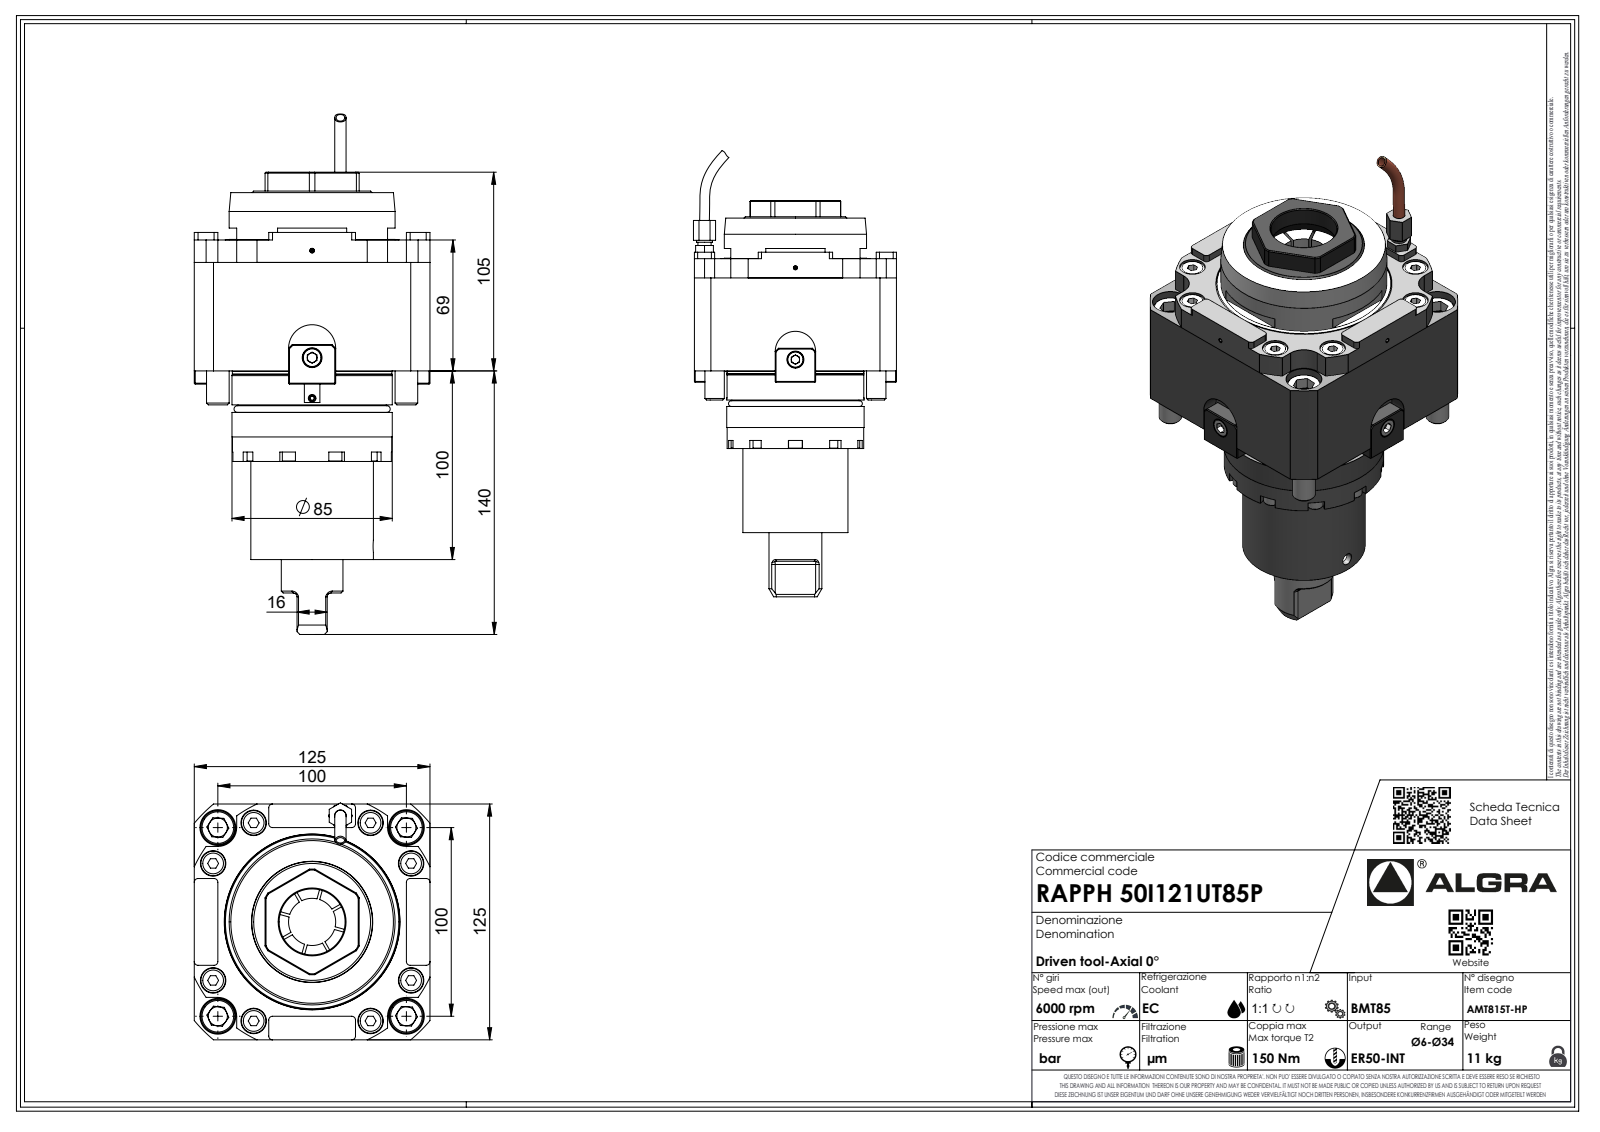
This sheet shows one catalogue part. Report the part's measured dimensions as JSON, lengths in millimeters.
{"part_name": "RAPPH50I121UT85P", "step_written_by": "SolidWorks 2023 (AUTOMOTIVE_DESIGN)", "units": "millimeters", "bodies": {"solids": 1, "faces": 591, "planar": 404, "cylindrical": 80, "other": 107}, "overall_size": [275.99, 125.59, 125], "volume_mm3": 1719000, "surface_area_mm2": 107858, "round_holes": [[2.1, 1]], "round_bosses_or_shafts": [[12, 4], [88, 1], [85, 1], [65, 1], [32.7, 1], [9.8, 1], [8.15, 1], [6.37, 1]], "partial_cylinders_radius": [[2, 22], [0.33, 7], [0.52, 7], [3.7, 7], [10, 4], [0.21, 1], [28, 1], [69, 1]], "face_to_face_distances": [125, 69.5, 48, 25, 100, 94.5, 169.5, 194.5, 52, 117.5]}
